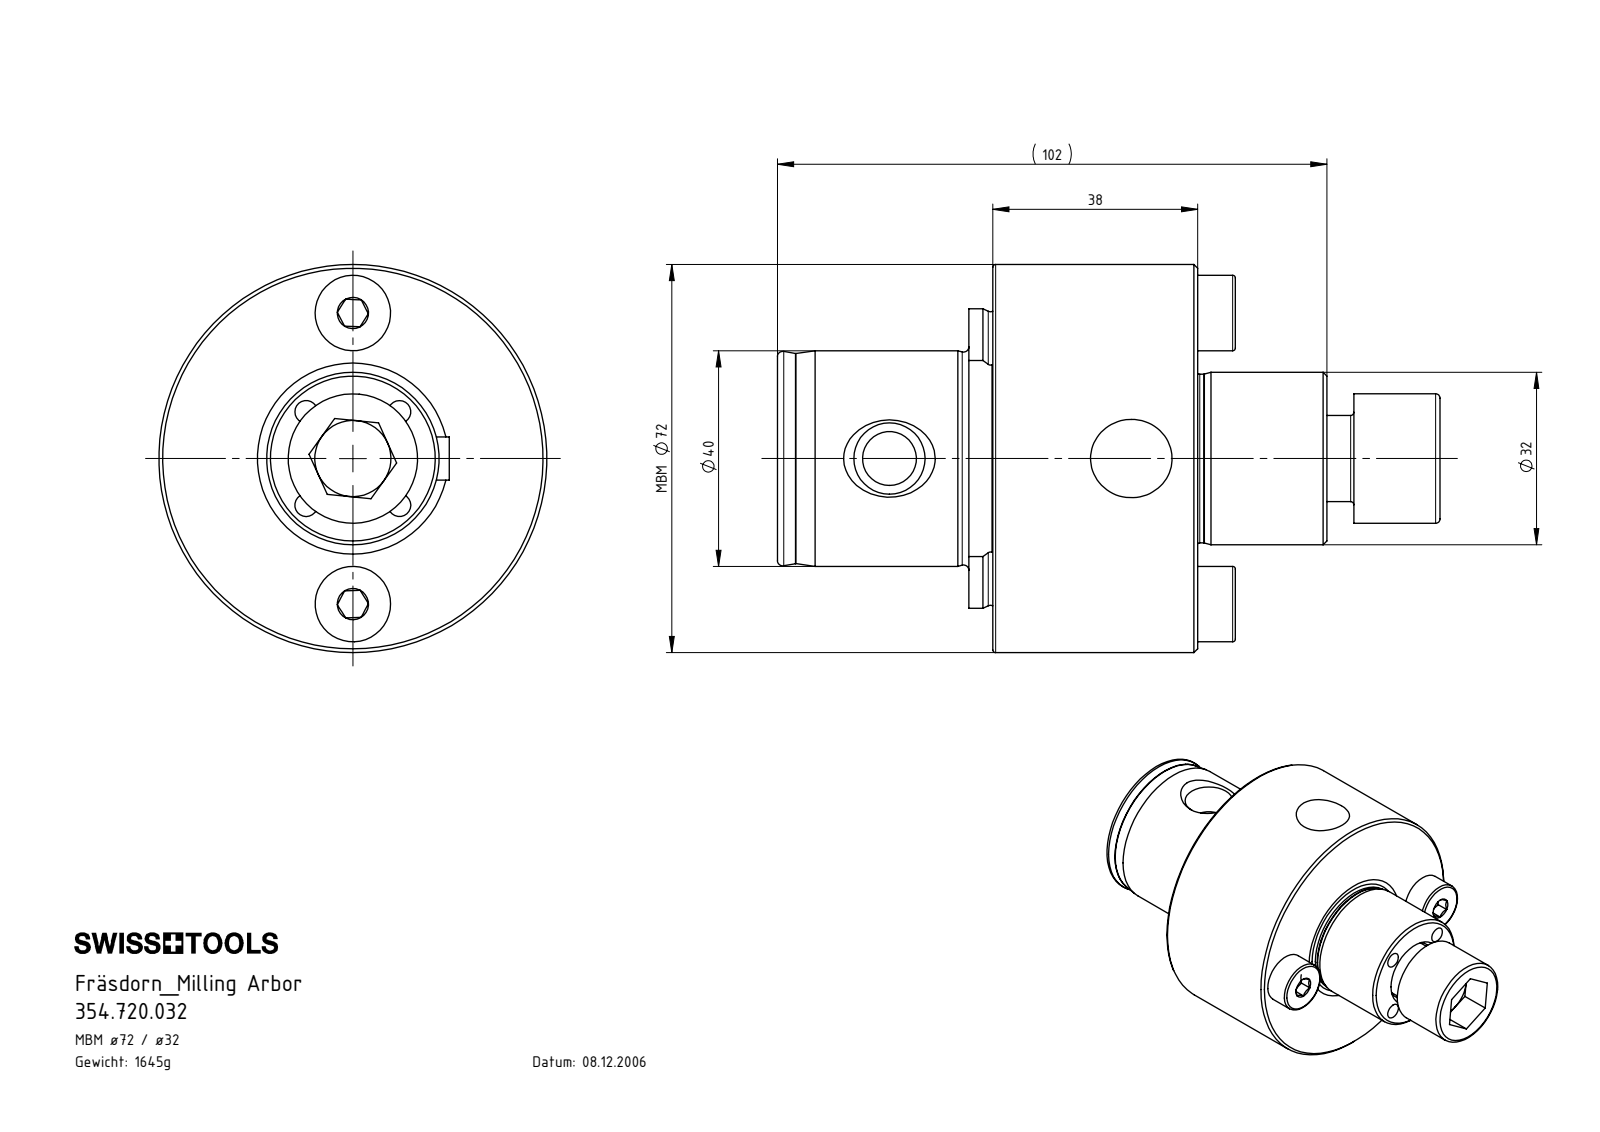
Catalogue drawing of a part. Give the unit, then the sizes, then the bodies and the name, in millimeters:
Units: millimetres
Overall size (bounding box): 119 × 72 × 72
Round holes (diameter × count): ⌀3 ×12, ⌀5 ×4, ⌀6.5 ×1, ⌀10 ×1, ⌀11 ×1, ⌀14 ×1, ⌀17 ×1, ⌀23 ×1
Round bosses / shafts (diameter × count): ⌀72 ×1, ⌀42 ×1, ⌀40 ×1, ⌀32 ×1, ⌀31.3 ×1, ⌀24 ×1, ⌀16 ×1, ⌀10 ×1
Partial cylindrical surfaces — rounded edges, fillets, slot ends (radius × count): R4 ×4, R7 ×1, R27.77 ×1
Main face-to-face distances: 10, 38, 41, 79, 69, 14, 40, 78, 119, 109
Hole centre spacings: 14.5, 25.11, 2.39, 12.25, 12.84, 14.19, 14.49, 14.51
Volume: 226 648 mm³ · Surface area: 44 528 mm²
Bodies: 8 solids, 194 faces (76 planar, 65 cylindrical, 53 other)
Part name (STEP PRODUCT): MB7-D32.K01.038_C; D32-ER3.001.020_A; D32-ER2.002.014_A; D32-ER1.K62.010_A (+4 more)
STEP written by: SolidWorks 2017 (AUTOMOTIVE_DESIGN)
